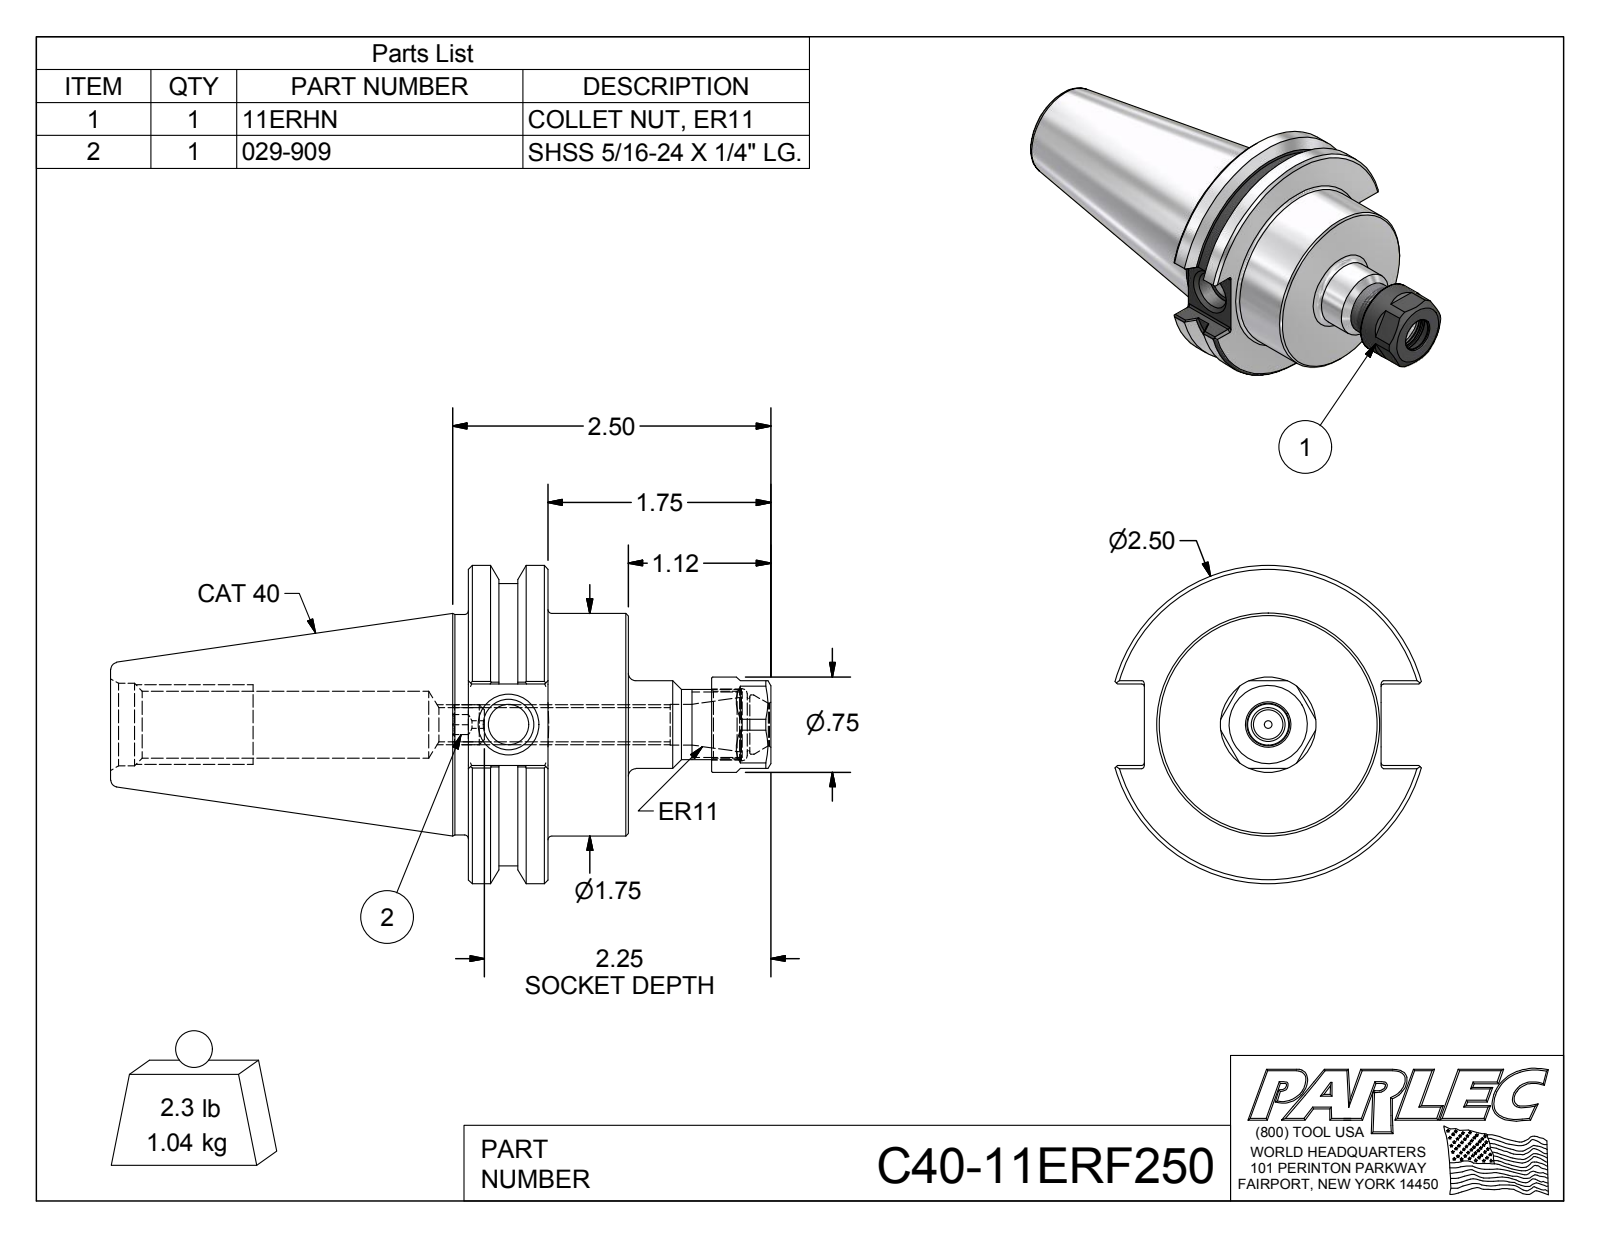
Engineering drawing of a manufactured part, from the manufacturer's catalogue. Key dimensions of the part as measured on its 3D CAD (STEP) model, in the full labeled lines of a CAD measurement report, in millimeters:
Part name (STEP PRODUCT): C40-11ERF250; C40-11ER2-1; 029-909; 11ERHN
STEP written by: Autodesk Inventor 2012 (AUTOMOTIVE_DESIGN)
Units: millimetres
Bodies: 3 solids, 148 faces (63 planar, 35 cylindrical, 50 other)
Overall size (bounding box): 131.7 × 63.5 × 61.1
Volume: 132 100 mm³ · Surface area: 25 750 mm²
Round holes (diameter × count): ⌀1.5 ×1, ⌀6.8 ×1, ⌀8 ×1, ⌀8.1 ×1, ⌀8.5 ×1, ⌀10.1 ×1, ⌀11.8 ×1, ⌀13.3 ×1, ⌀13.4 ×1, ⌀14.4 ×1, ⌀16.5 ×1
Round bosses / shafts (diameter × count): ⌀63.5 ×1, ⌀56.4 ×1, ⌀44.5 ×1, ⌀43.9 ×1, ⌀19.1 ×1, ⌀17.5 ×1, ⌀14 ×1, ⌀8 ×1
Partial cylindrical surfaces — rounded edges, fillets, slot ends (radius × count): R0.5 ×12
Main face-to-face distances: 31.9, 15.9, 16, 16.3, 47.2, 60.3, 44.5, 28.4, 71.4, 87.3
